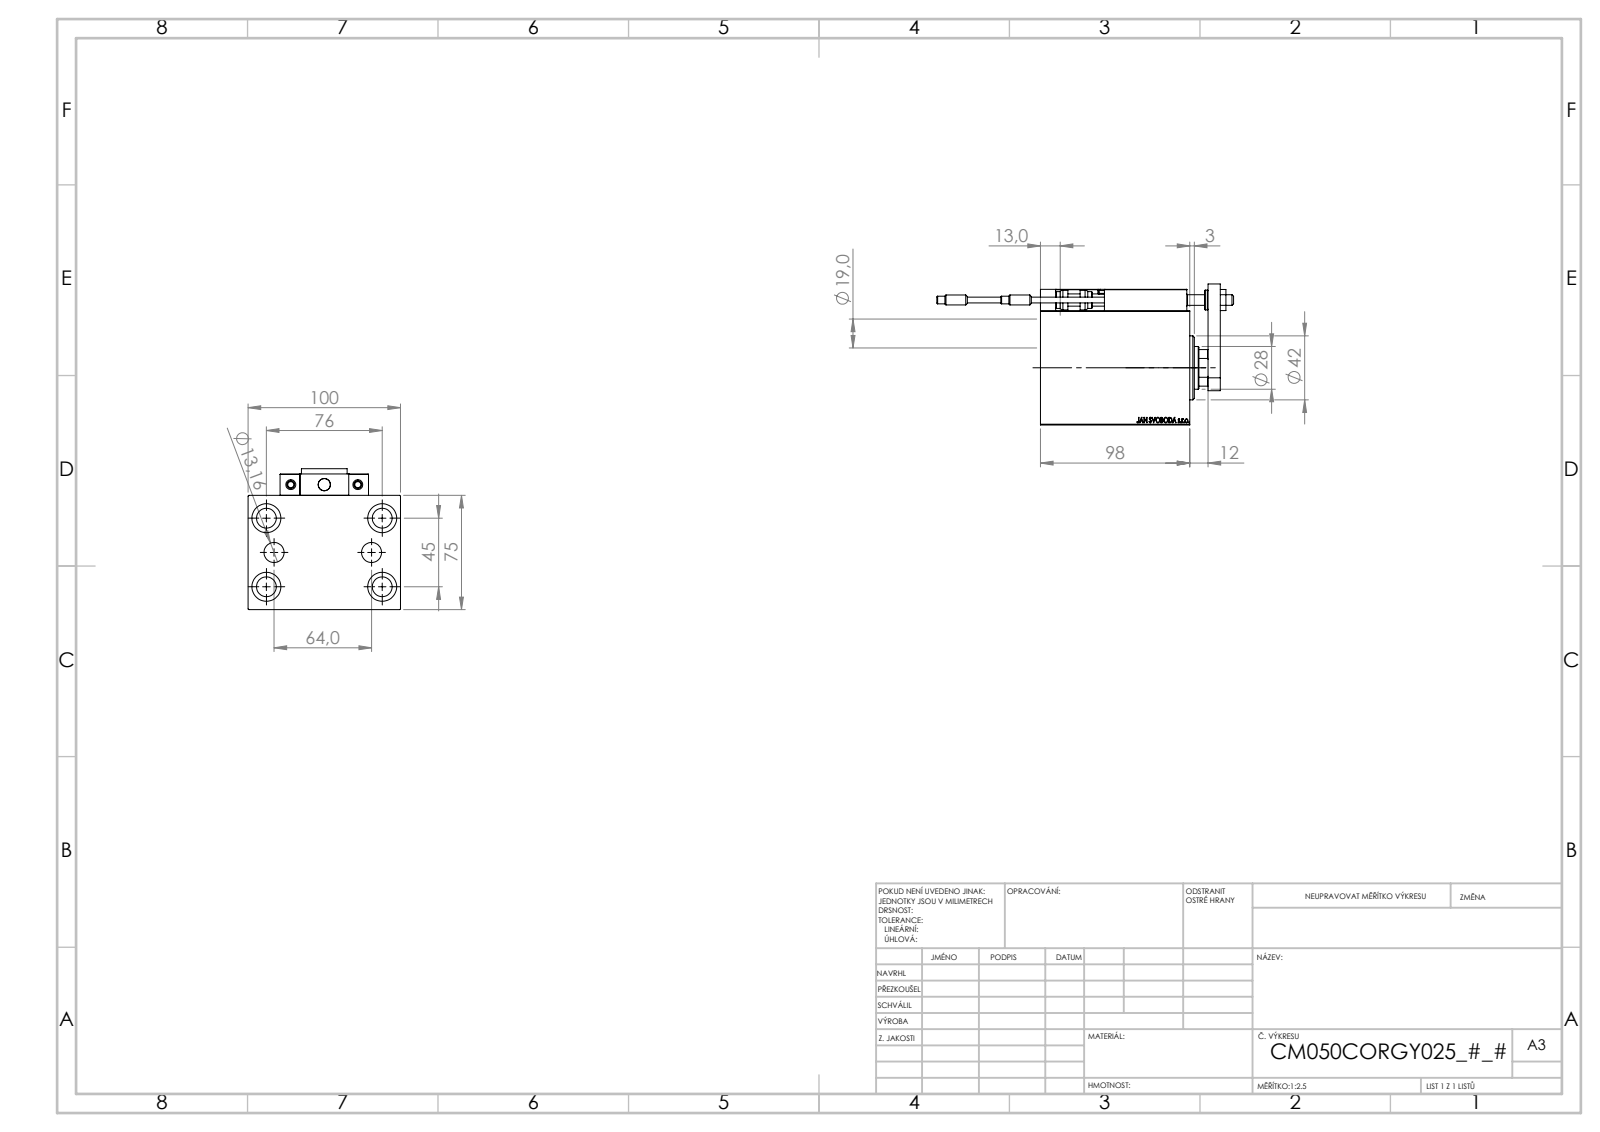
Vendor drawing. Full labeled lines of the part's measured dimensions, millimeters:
Part name (STEP PRODUCT): ALLEN BOLT D8; TYC_L79; Block; SWITCH DIM B,W (+7 more)
STEP written by: SolidWorks 2019 (CONFIG_CONTROL_DESIGN)
Units: millimetres
Bodies: 23 solids, 1297 faces (561 planar, 190 cylindrical, 546 other)
Overall size (bounding box): 194.7 × 100 × 92.5
Volume: 688 932 mm³ · Surface area: 132 423 mm²
Round holes (diameter × count): ⌀8 ×5, ⌀3.2 ×4, ⌀4 ×4, ⌀13 ×4, ⌀19 ×4, ⌀5 ×2, ⌀13.16 ×2, ⌀7 ×1, ⌀18.5 ×1, ⌀20 ×1, ⌀28 ×1, ⌀31.5 ×1
Round bosses / shafts (diameter × count): ⌀5 ×4, ⌀6.5 ×2, ⌀3.8 ×2, ⌀42 ×1, ⌀13 ×1, ⌀11 ×1
Partial cylindrical surfaces — rounded edges, fillets, slot ends (radius × count): R0.3 ×30, R3 ×2, R13.5 ×1
Main face-to-face distances: 75, 100, 14, 98, 12, 84, 25, 24, 32, 8
Hole centre spacings: 44.16, 11.37, 20, 23.05, 23.56, 29.59, 29.69, 36.06
